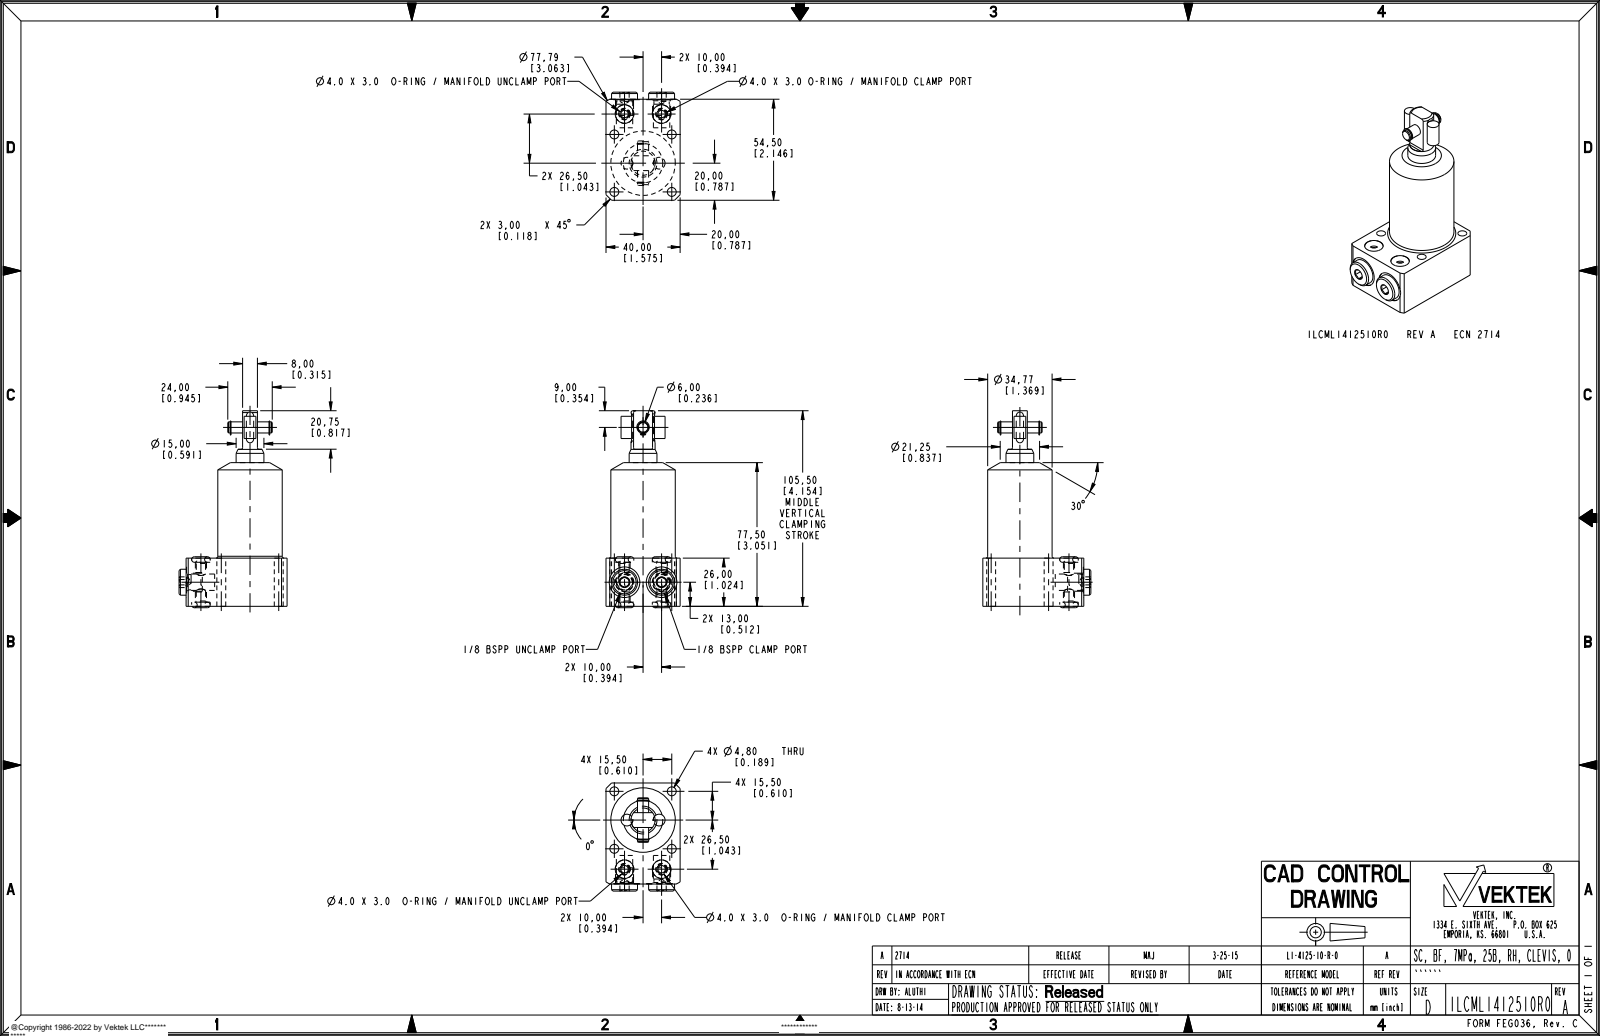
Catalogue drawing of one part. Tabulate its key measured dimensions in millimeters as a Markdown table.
| quantity | value |
| --- | --- |
| part name | ILCML1412510R0 |
| STEP written by | PRO/ENGINEER BY PARAMETRIC TECHNOLOGY CORPORATION, 2013320 (AUTOMOTIVE_DESIGN) |
| units | millimeters |
| bodies | 7 solids, 234 faces (80 planar, 98 cylindrical, 56 other) |
| overall size | 106.25 × 58.31 × 40 |
| volume | 105 212 mm³ |
| surface area | 21 943 mm² |
| round holes (diameter × count) | 4.8 × 4, 0.66 × 2, 5 × 2, 8.84 × 2, 10 × 2, 16.5 × 2 |
| round bosses / shafts (diameter × count) | 6 × 3, 14 × 2, 9.73 × 2, 8.25 × 2, 6.35 × 2, 34.77 × 1, 15 × 1, 13 × 1 |
| partial cylindrical surfaces (radius × count) | 0.66 × 2, 0.8 × 2, 1.07 × 2, 3.17 × 2, 38.9 × 1 |
| main face-to-face distances | 40, 26, 54.5, 16, 8, 24, 58.31, 3.81, 2.25, 23.75 |
| hole center spacings | 31, 12.3, 20, 27.77, 42.36, 43.84, 49.14, 80.55 |
